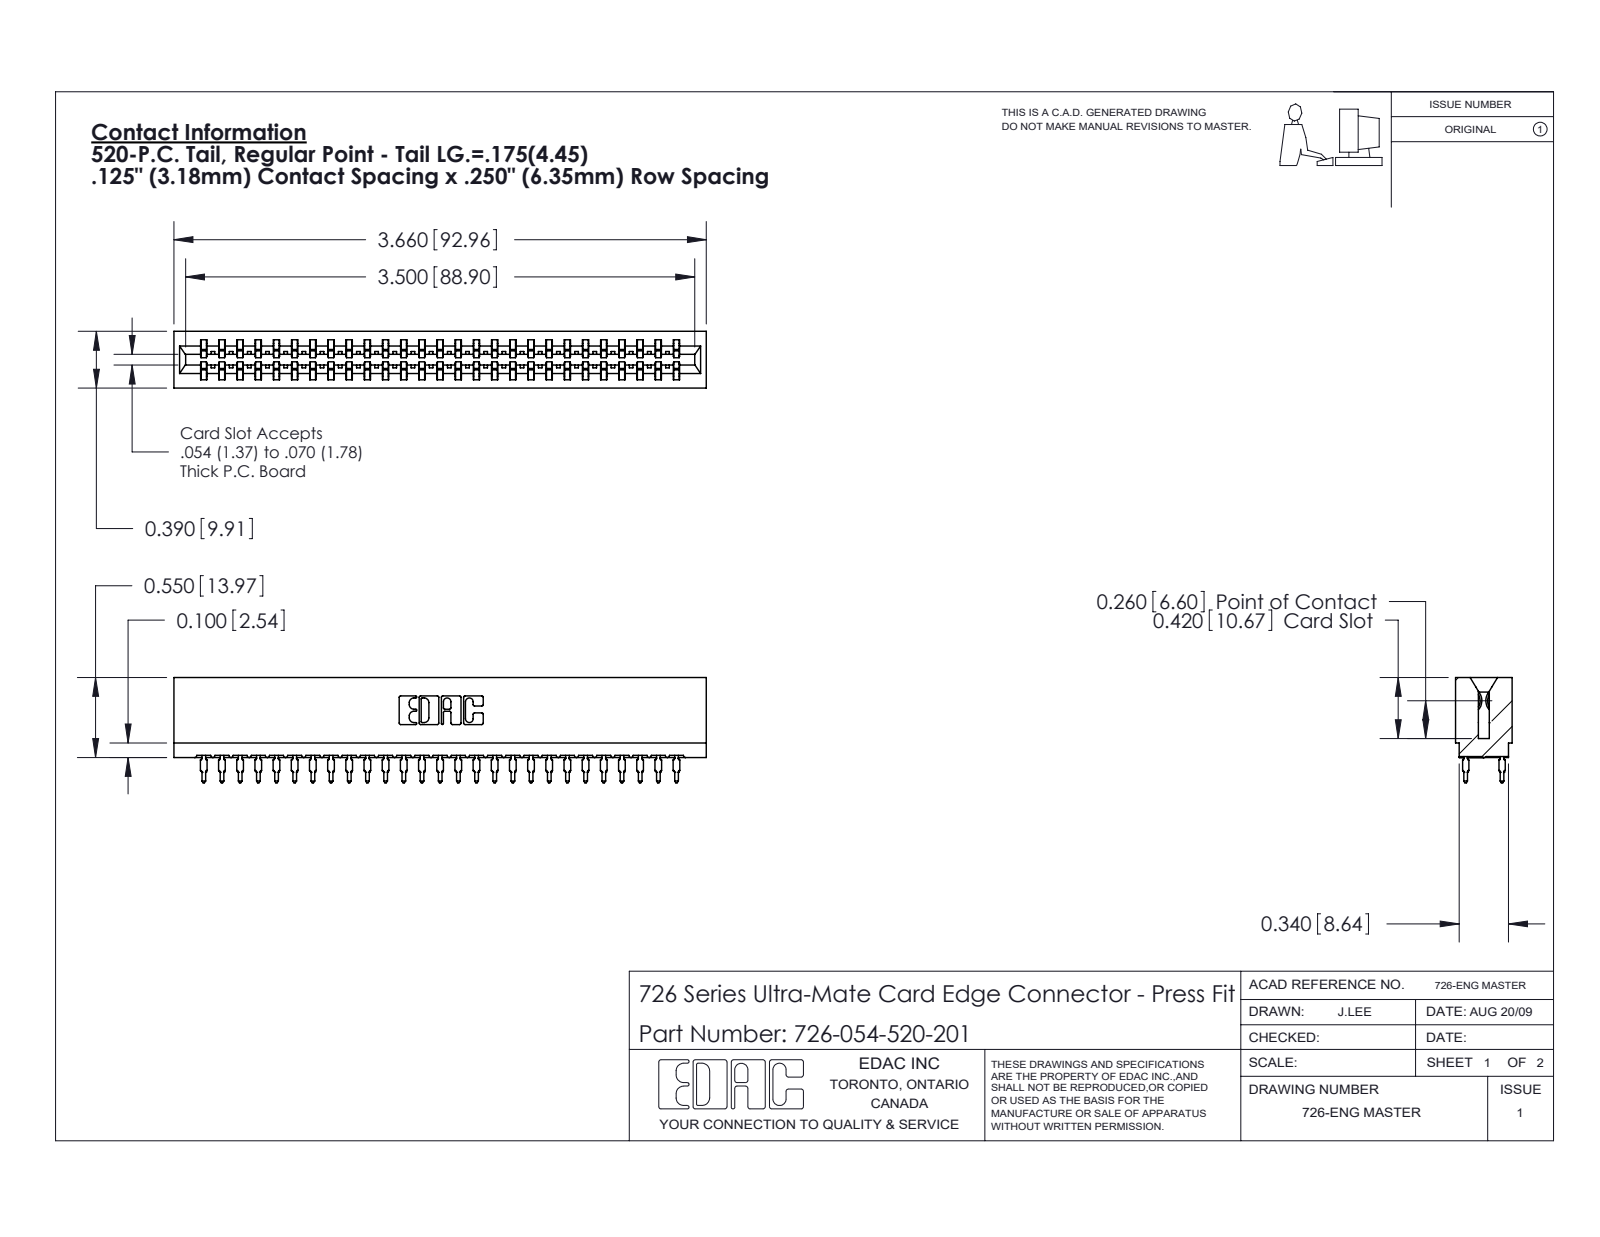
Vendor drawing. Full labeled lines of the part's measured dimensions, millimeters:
Part name (STEP PRODUCT): 746-292-001_520; 726-054-520-201; 726 Part_.515 Slot Depth - 01
STEP written by: SolidWorks 2020 (CONFIG_CONTROL_DESIGN)
Units: millimetres
Bodies: 55 solids, 4930 faces (2539 planar, 987 cylindrical, 1404 other)
Overall size (bounding box): 93 × 18.4 × 9.9
Volume: 8 590 mm³ · Surface area: 13 810 mm²
Partial cylindrical surfaces — rounded edges, fillets, slot ends (radius × count): R0.5 ×108, R0.4 ×28, R0.3 ×22, R0.1 ×8, R0.3 ×8, R0.2 ×6, R0.8 ×6, R0.7 ×3
Main face-to-face distances: 1.4, 8.5, 6.4, 9.9, 0.6, 7.8, 7, 2.1, 12.7, 9.3
